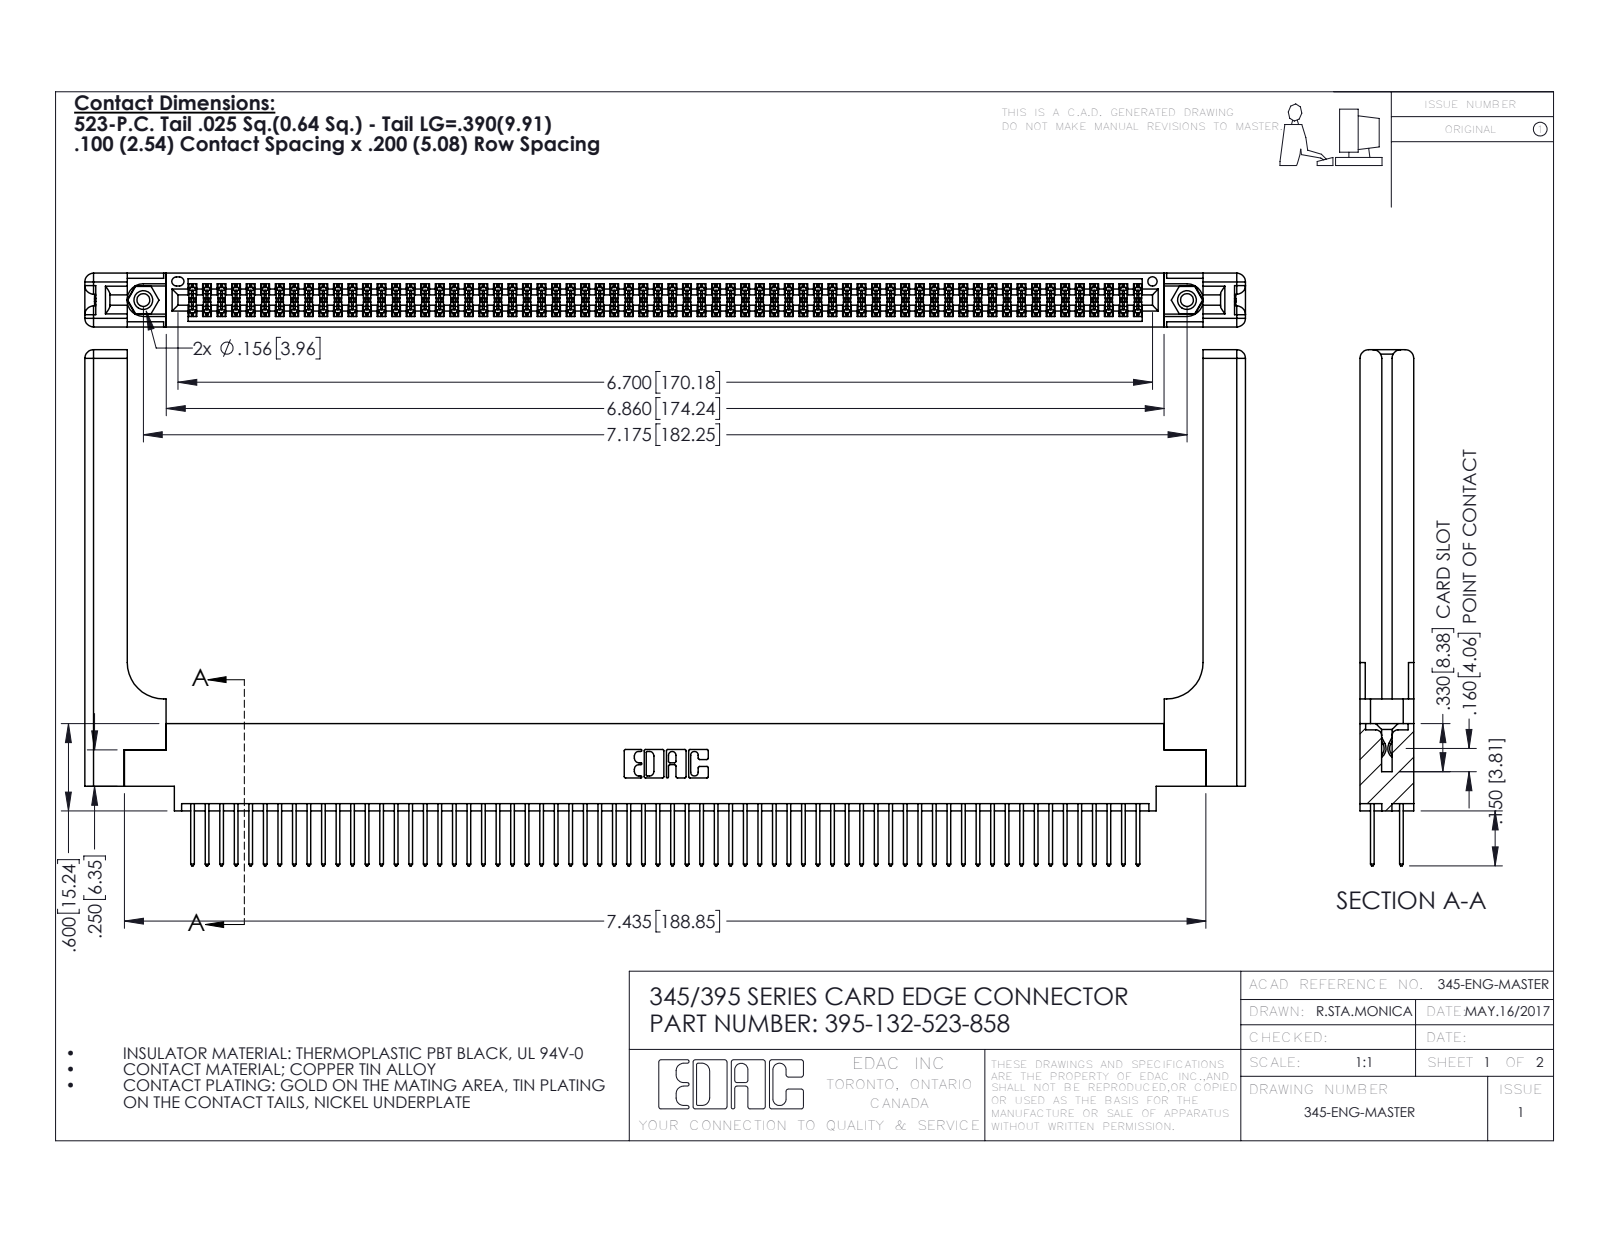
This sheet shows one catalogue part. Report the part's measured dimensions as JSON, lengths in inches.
{"part_name": "345-250-001_345-250-001-102; 345-220-058_345-220-058; 395-132-523-858; 345 Part_0.170 Offset - 0.156 Dia-TH (+1 more)", "step_written_by": "SolidWorks 2016 (CONFIG_CONTROL_DESIGN)", "units": "inches", "bodies": {"solids": 137, "faces": 6986, "planar": 4588, "cylindrical": 2338, "other": 60}, "overall_size": [7.979, 3.547, 0.37], "volume_in3": 1.742, "surface_area_in2": 56.64, "round_holes": [[0.089, 2], [0.125, 2], [0.156, 2], [0.064, 1]], "round_bosses_or_shafts": [[0.155, 2]], "partial_cylinders_radius": [[0.006, 198], [0.01, 132], [0.01, 22], [0.06, 16], [0.007, 6], [0.031, 6], [0.026, 3], [0.014, 2]], "face_to_face_distances": [0.072, 0.298, 0.37, 0.098, 0.272, 0.025, 0.2, 0.225, 0.175, 0.148], "hole_center_spacings": [0.27, 6.939, 7.175]}
